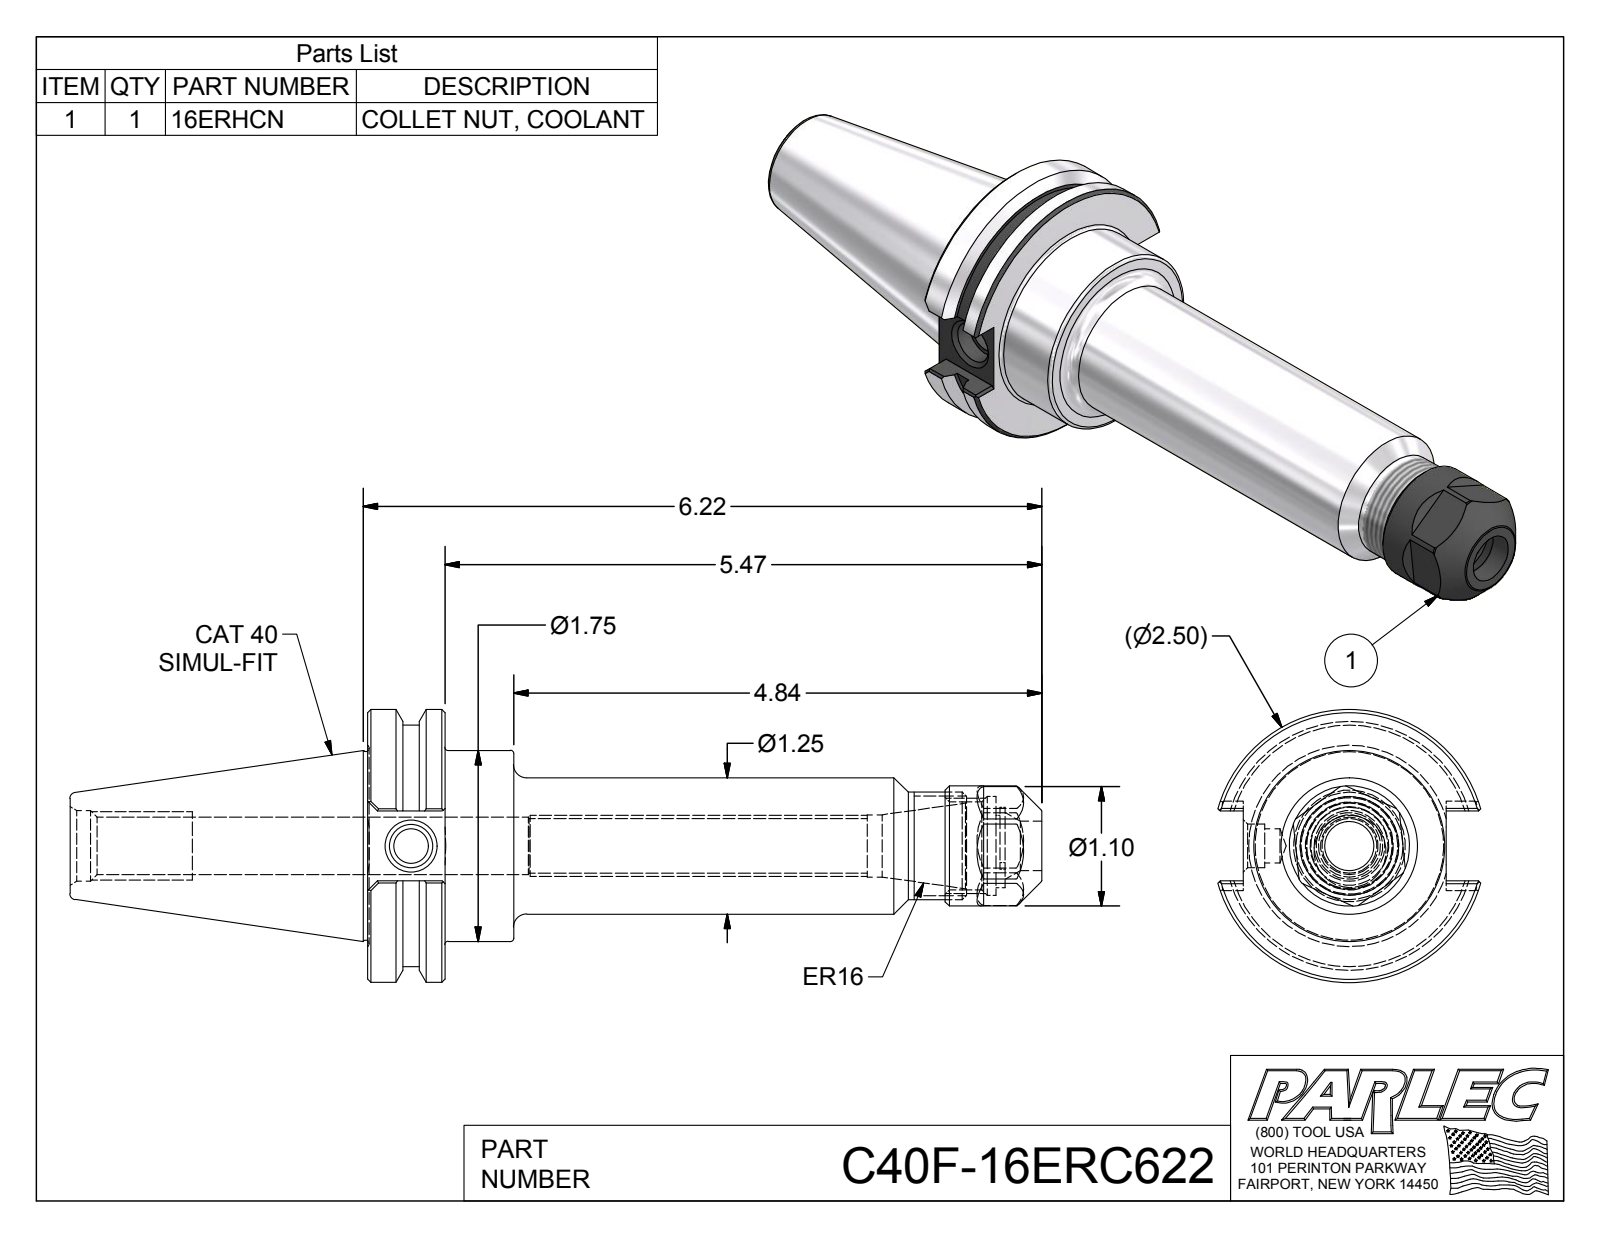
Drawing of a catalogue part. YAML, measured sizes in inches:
part_name: "C40F-16ERC622; C40F-20ER6-1; 16ERHCN"
step_written_by: "Autodesk Inventor 2018 (AUTOMOTIVE_DESIGN)"
units: inches
bodies: {solids: 2, faces: 112, planar: 50, cylindrical: 21, other: 41}
overall_size: [8.908, 2.5, 2.406]
volume: 11.91
surface_area: 64.19
round_holes:
  - {diameter: 0.315, count: 1}
  - {diameter: 0.399, count: 1}
  - {diameter: 0.453, count: 1}
  - {diameter: 0.502, count: 1}
  - {diameter: 0.527, count: 1}
  - {diameter: 0.57, count: 1}
  - {diameter: 0.648, count: 1}
  - {diameter: 0.661, count: 1}
  - {diameter: 0.807, count: 1}
  - {diameter: 0.906, count: 1}
round_bosses_or_shafts:
  - {diameter: 2.5, count: 1}
  - {diameter: 2.215, count: 1}
  - {diameter: 1.75, count: 1}
  - {diameter: 1.25, count: 1}
  - {diameter: 1.102, count: 1}
  - {diameter: 0.984, count: 1}
partial_cylinders:
  - {radius: 0.354, count: 1}
face_to_face_distances: [0.71, 1.34, 0.63, 0.979, 5.759, 5.049, 4.419, 1.86, 0.64, 5.294]
hole_center_spacings: [0.051]
